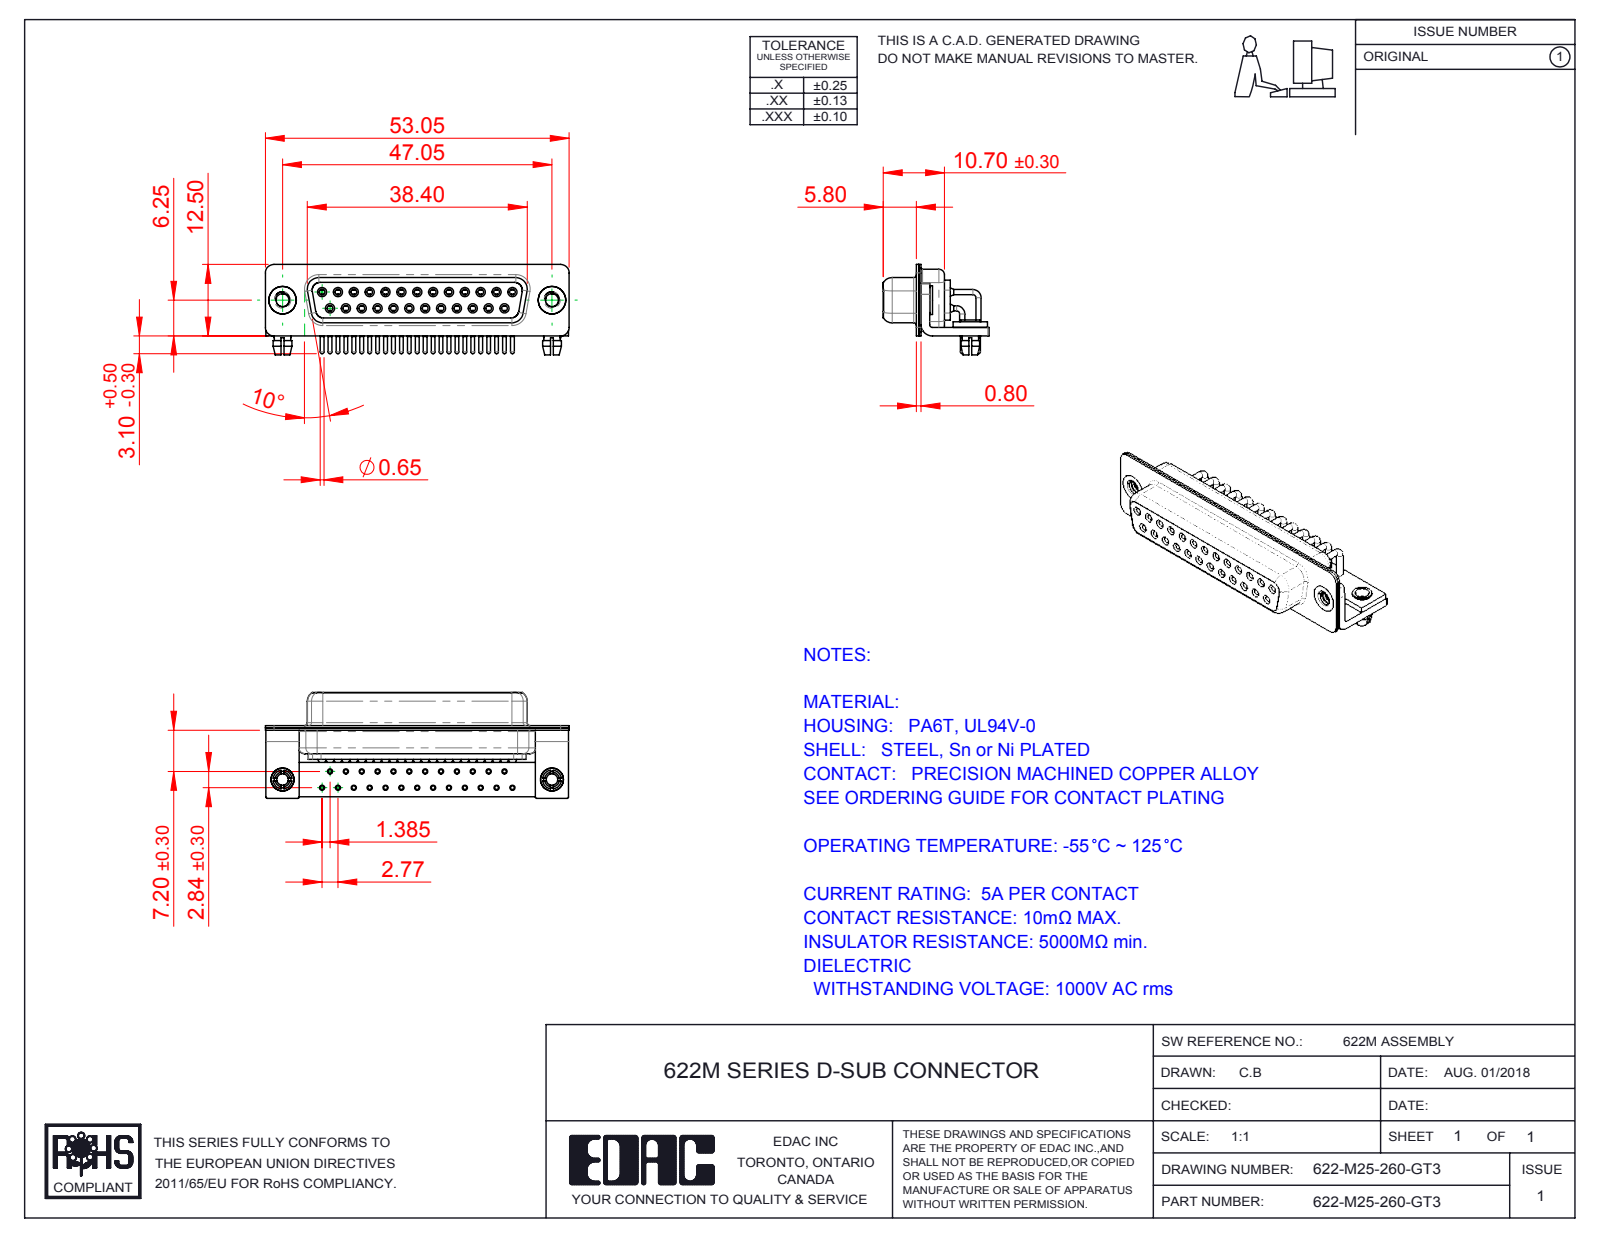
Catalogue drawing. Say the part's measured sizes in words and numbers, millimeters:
The part is named "622M Contact Row 1; 622M Shell Rear_25 Contacts; 622M Shell Front_25 Contacts; 622-M25-260-GT3 (+6 more)". Its 3-D file was written by "SolidWorks 2016 (CONFIG_CONTROL_DESIGN)". It is 35 solids with 1796 faces: 516 planar, 816 cylindrical and 464 other. Overall it measures 53.05 by 18.5 by 15.8 millimeters. Its volume is 4 408 cubic millimeters and its surface area 11 042 square millimeters. Round holes: 27 of diameter 2, 25 of diameter 0.9, 25 of diameter 1, 25 of diameter 1.1, 25 of diameter 1.7, 25 of diameter 1.8, 2 of diameter 2.26, 2 of diameter 2.5, 2 of diameter 3.2, 2 of diameter 4, 2 of diameter 4.8. Round bosses or shafts: 27 of diameter 0.9, 25 of diameter 1.6, 25 of diameter 1.5, 25 of diameter 0.65, 2 of diameter 5, 2 of diameter 4.9, 2 of diameter 4, 2 of diameter 3.4. Partial cylindrical surfaces (rounded edges, fillets, slot ends): 16 of radius 0.25, 16 of radius 1.5, 13 of radius 2, 8 of radius 1.35, 8 of radius 1.6, 5 of radius 0.5, 4 of radius 0.6, 4 of radius 0.65. The main face-to-face distances are 0.4, 2.3, 1.9, 1.45, 8.95, 0.85, 0.8, 6.2, 9.35, 1. The hole center spacings are 3.16, 2.77, 5.54, 8.31, 11.08, 13.85, 16.62, 5.04.
